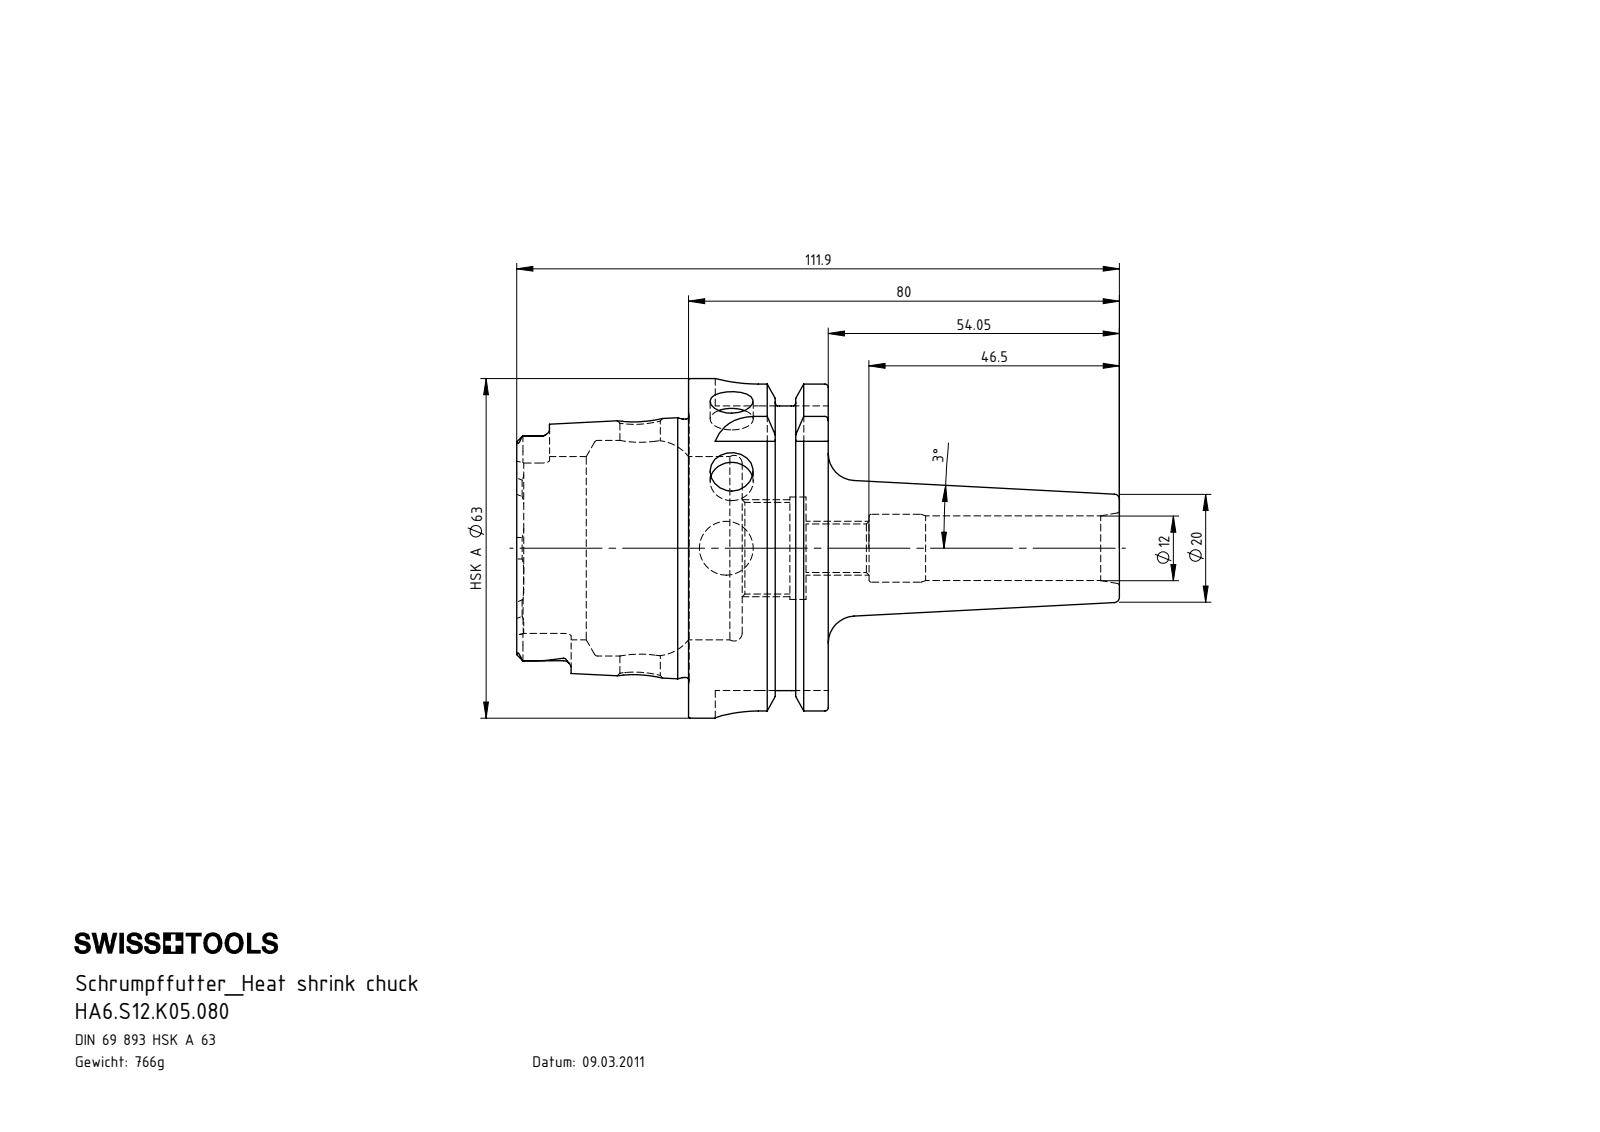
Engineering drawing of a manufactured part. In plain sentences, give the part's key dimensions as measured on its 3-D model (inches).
The part is named "HA6-S12.K05.080". Its 3-D file was written by "SolidWorks 2012 (AUTOMOTIVE_DESIGN)". It is 1 solid with 187 faces: 49 planar, 51 cylindrical and 87 other. Overall it measures 4.406 by 2.48 by 2.48 inches. Its volume is 6.135 cubic inches and its surface area 43.4 square inches. Round holes: 2 of diameter 0.315, 1 of diameter 0.295, 1 of diameter 0.354, 1 of diameter 0.394, 1 of diameter 0.472, 1 of diameter 0.496, 1 of diameter 0.669, 1 of diameter 0.748, 1 of diameter 1.339, 1 of diameter 1.575. Round bosses or shafts: 1 of diameter 2.48, 1 of diameter 2.163, 1 of diameter 1.887. Partial cylindrical surfaces (rounded edges, fillets, slot ends): 6 of radius 0.055, 4 of radius 0.113, 4 of radius 0.315. The main face-to-face distances are 1.022, 0.63, 0.392, 1.256, 1.648, 2.278, 2.079, 0.858, 0.467, 2.114.
